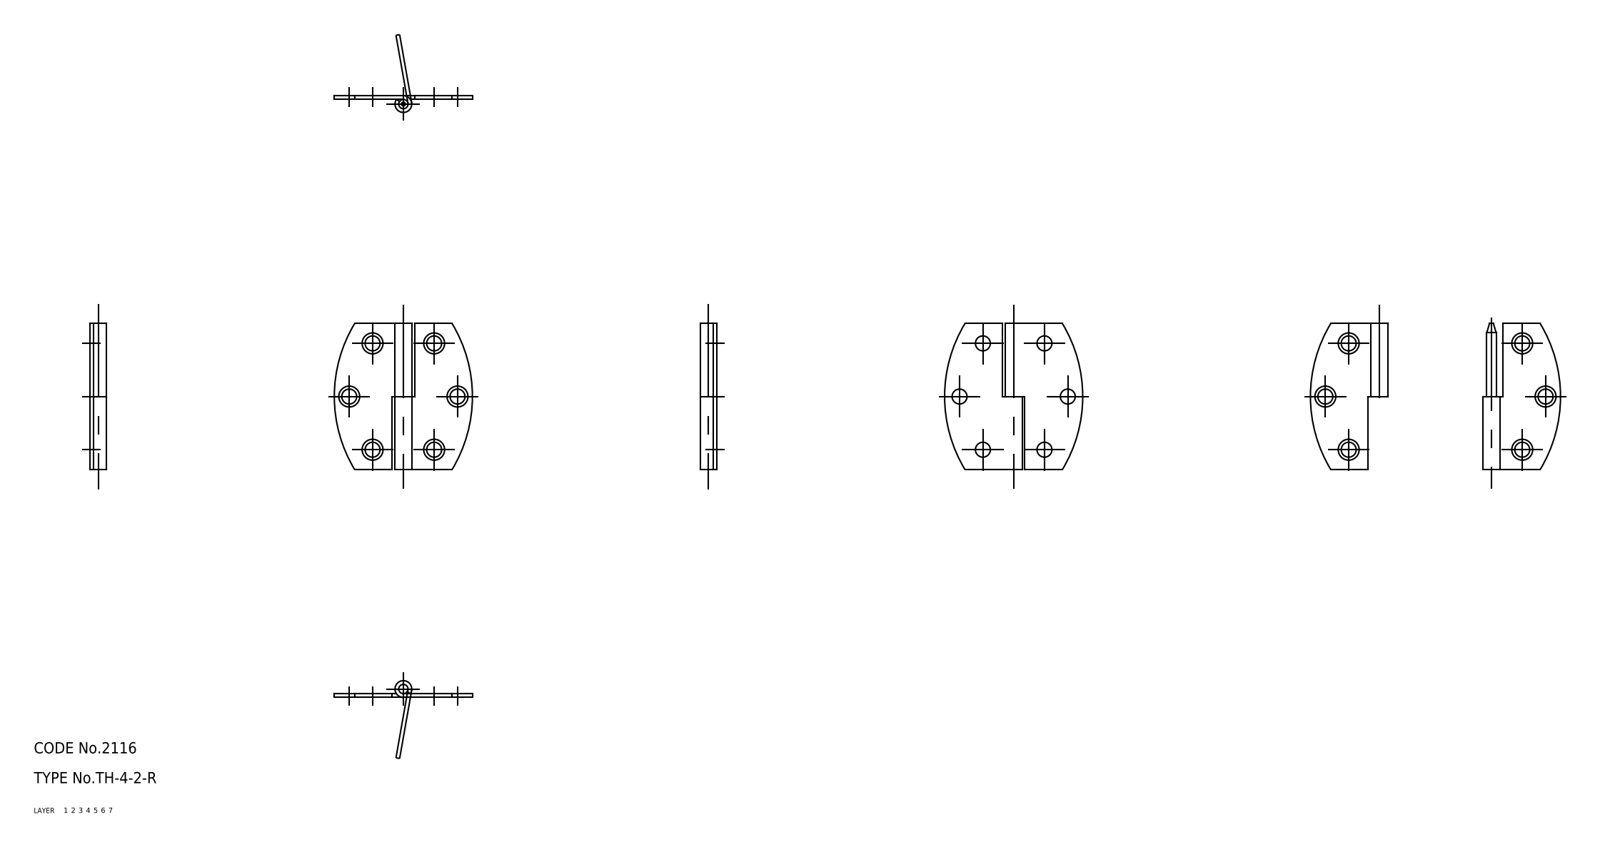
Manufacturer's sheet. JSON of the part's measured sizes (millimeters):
{"part_name": "shaft; hinge piece_B; hinge piece_A; TH_4_2_R_9202_36", "step_written_by": "CADfix (AUTOMOTIVE_DESIGN)", "units": "millimeters", "bodies": {"solids": 3, "faces": 50, "planar": 0, "cylindrical": 0, "other": 50}, "overall_size": [39.3, 37, 4.5], "volume_mm3": 1644, "surface_area_mm2": 3572}
